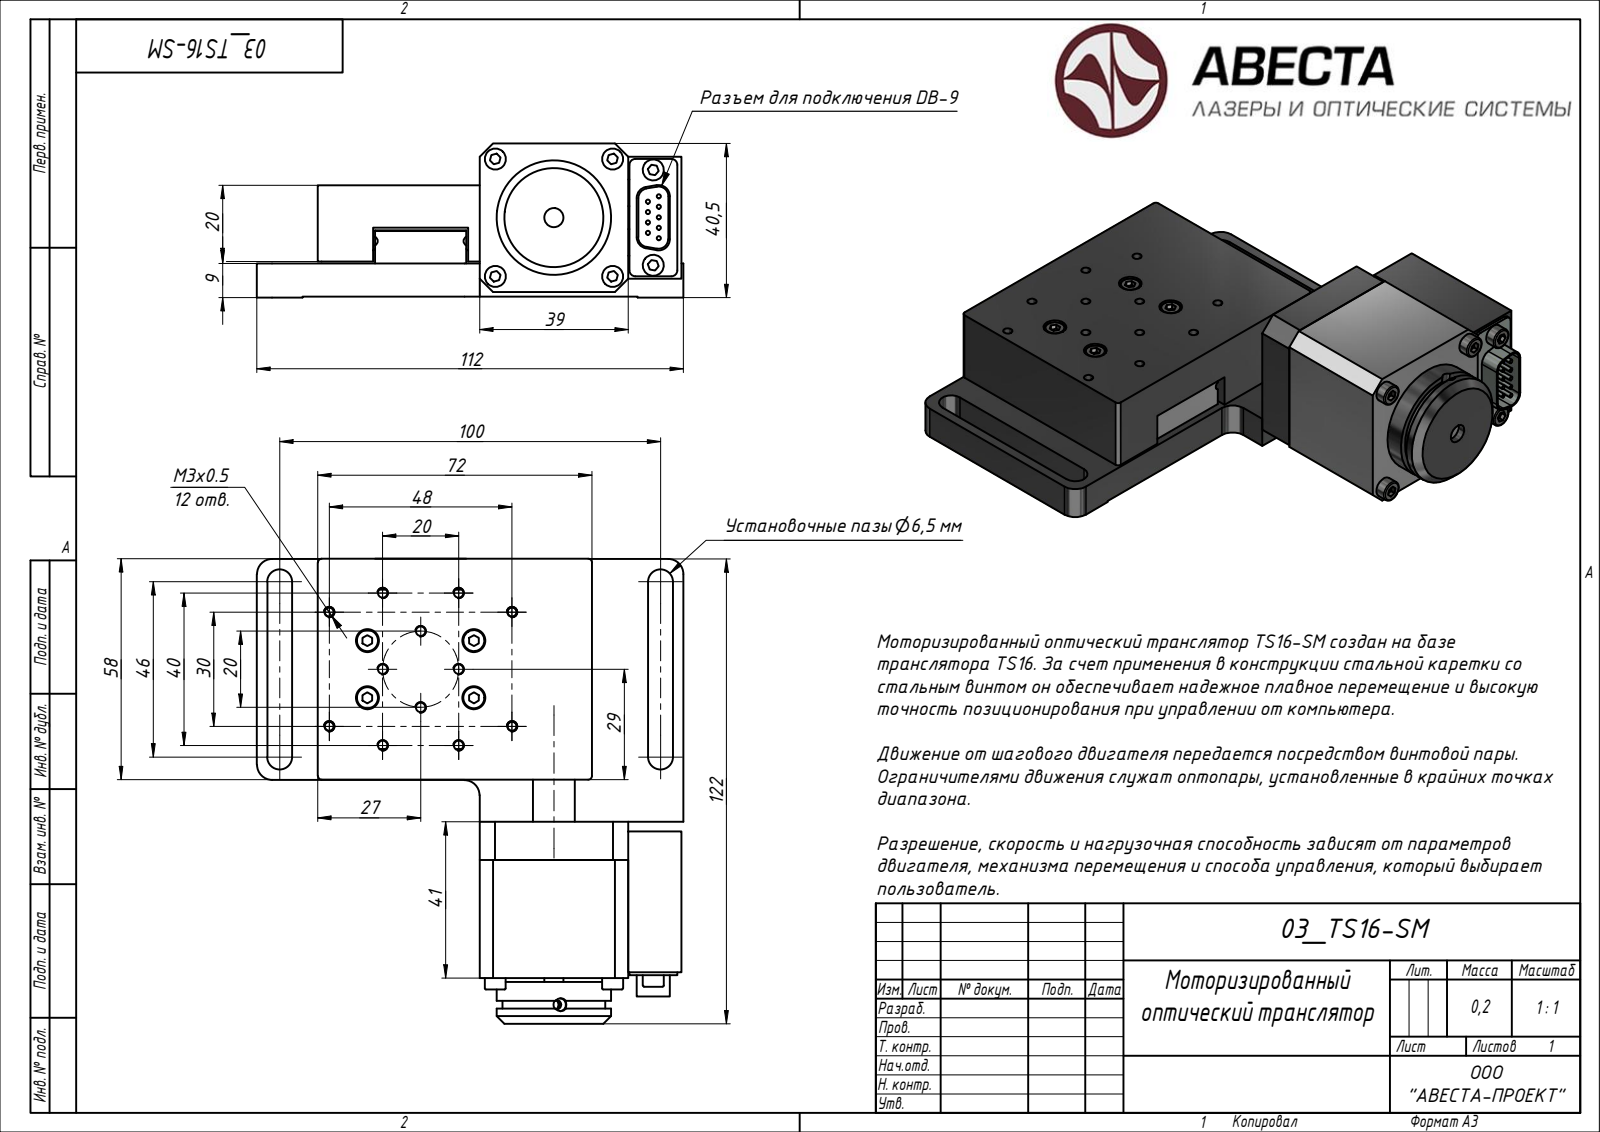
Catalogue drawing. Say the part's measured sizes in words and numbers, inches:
Its 3-D file was written by "Rhino 7.34 (AUTOMOTIVE_DESIGN)". It is 1 solid with 886 faces: 488 planar, 314 cylindrical and 84 other. Overall it measures 4.805 by 4.409 by 1.594 inches. Its volume is 11.88 cubic inches and its surface area 108.7 square inches. Round holes: 16 of diameter 0.097, 9 of diameter 0.087, 6 of diameter 0.236, 2 of diameter 0.062, 2 of diameter 0.106, 2 of diameter 0.128, 2 of diameter 0.177, 2 of diameter 0.197, 2 of diameter 0.307, 1 of diameter 0.062, 1 of diameter 0.097, 1 of diameter 0.134. Round bosses or shafts: 12 of diameter 0.217, 9 of diameter 0.042, 4 of diameter 0.118, 4 of diameter 0.079, 2 of diameter 0.157, 1 of diameter 1.181, 1 of diameter 0.472, 1 of diameter 0.433. Partial cylindrical surfaces (rounded edges, fillets, slot ends): 20 of radius 0.079, 16 of radius 0.118, 9 of radius 0.039, 8 of radius 0.048, 8 of radius 0.048, 8 of radius 0.062, 4 of radius 0.048, 4 of radius 0.083. The main face-to-face distances are 0.343, 1.15, 0.807, 0.531, 0.059, 0.63, 0.295, 0.551, 0.315, 0.433. The hole center spacings are 0.197, 0.108, 0.124, 0.787, 0.396, 0.517, 1.065, 1.094.
